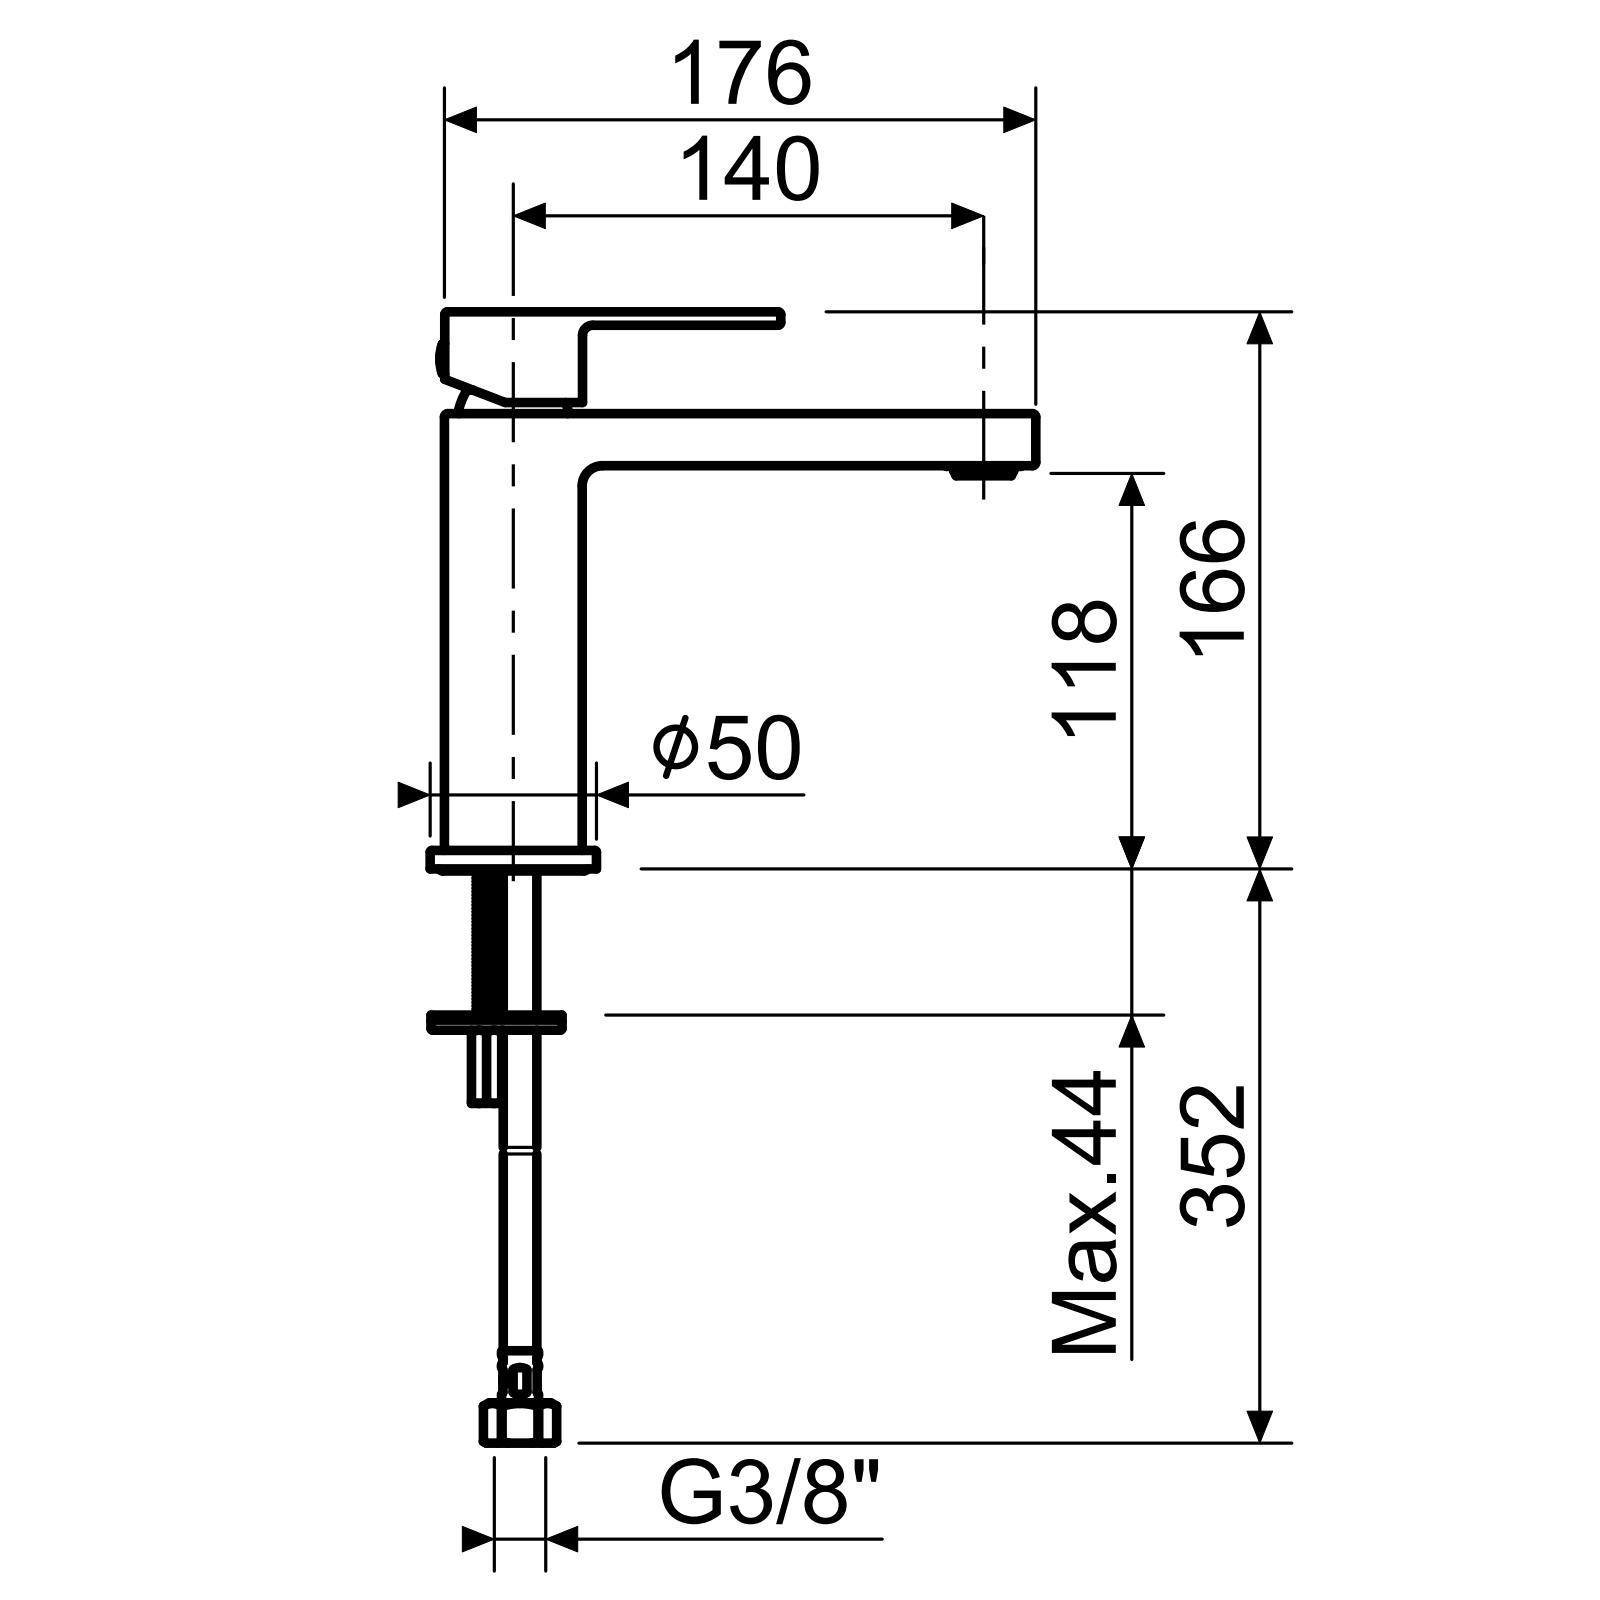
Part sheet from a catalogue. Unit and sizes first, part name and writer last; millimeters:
Units: millimetres
Overall size (bounding box): 180 × 167 × 50
Round holes (diameter × count): ⌀4.5 ×1, ⌀4.5 ×1, ⌀8.35 ×1, ⌀10 ×1, ⌀22.5 ×1
Round bosses / shafts (diameter × count): ⌀24 ×1, ⌀18.7 ×1, ⌀7 ×1, ⌀6.5 ×1
Partial cylindrical surfaces — rounded edges, fillets, slot ends (radius × count): R0.5 ×34
Main face-to-face distances: 35, 15, 130, 115, 32, 162, 47, 42.5, 5, 4.5
Hole centre spacings: 140
Volume: 296 134 mm³ · Surface area: 58 583 mm²
Bodies: 6 solids, 741 faces (657 planar, 55 cylindrical, 29 other)
Part name (STEP PRODUCT): BODY_LAVABO_QUADRA_1; AERATORE_SLIM_NEOPERL_M24X1_A_1; GHIERA_CARTUCCIA_DA_25_1; LEVA_DA_35_QUADRA_1 (+4 more)
STEP written by: CREO PARAMETRIC BY PTC INC, 2020281 (CONFIG_CONTROL_DESIGN)
